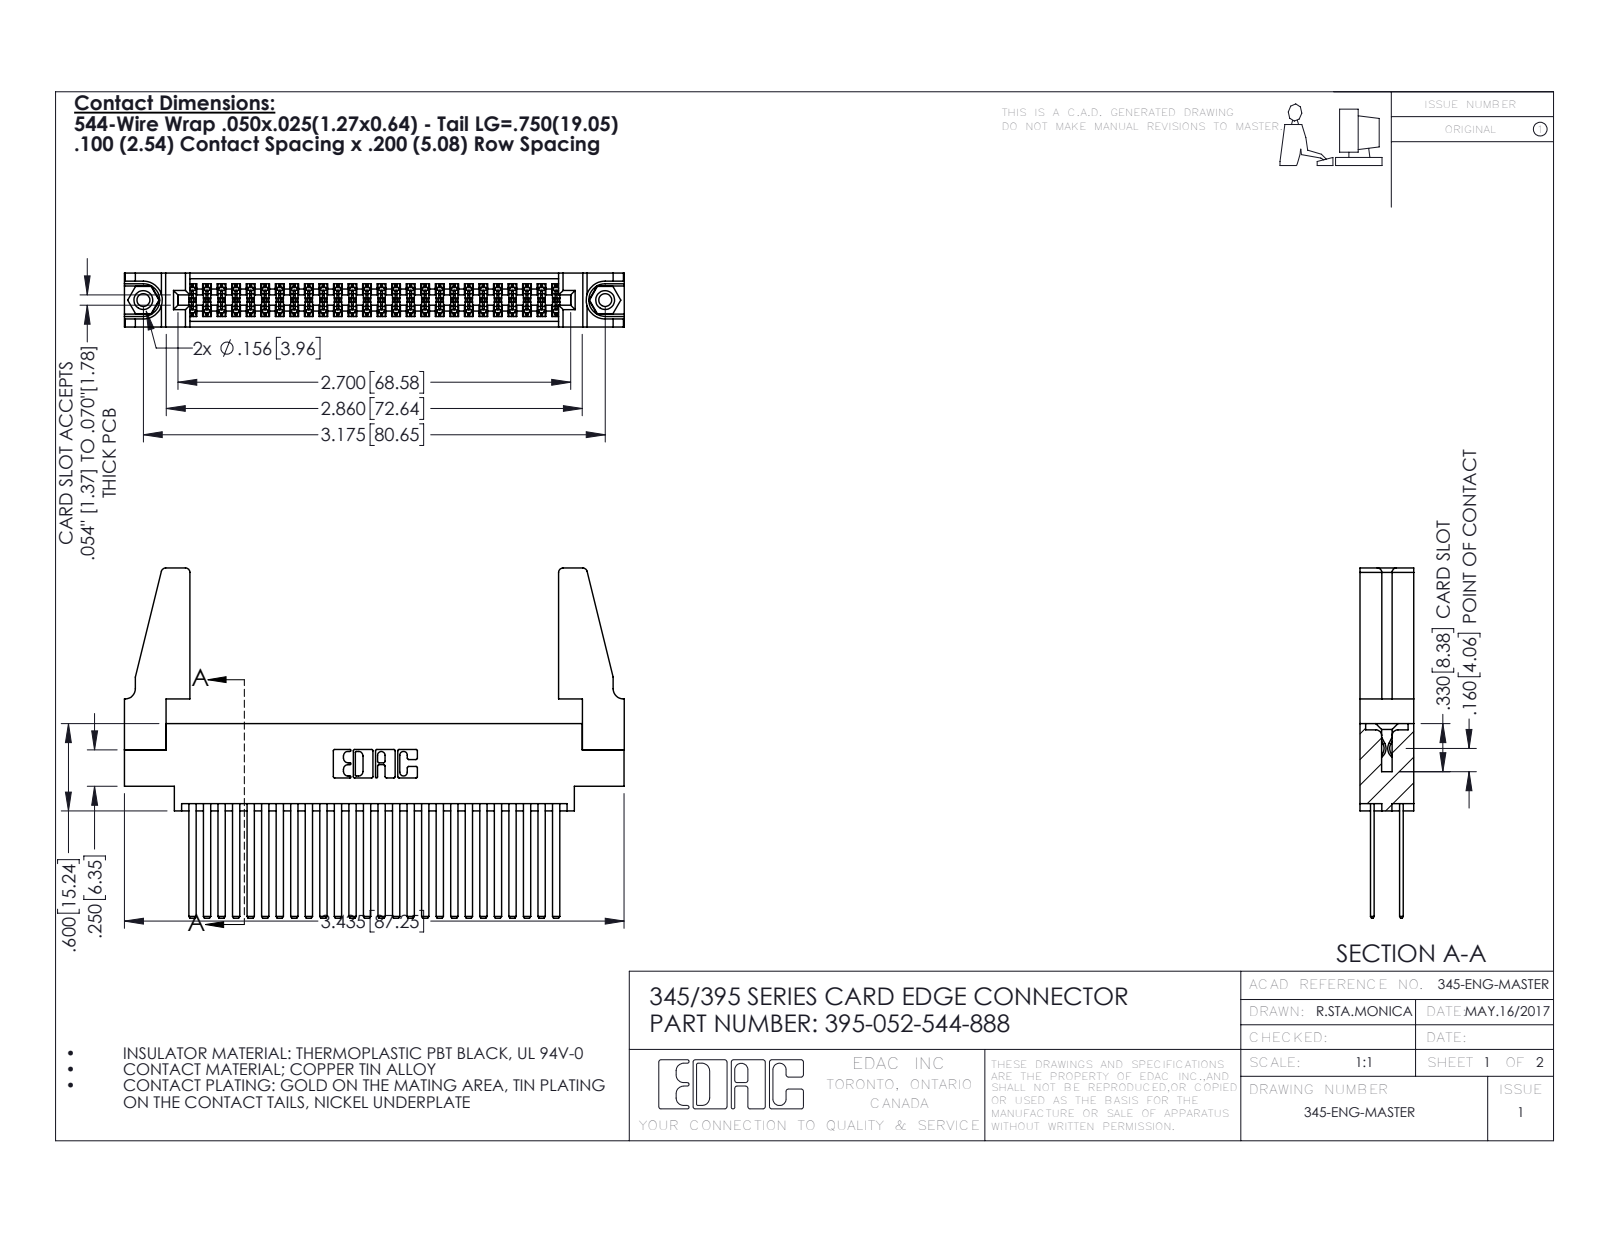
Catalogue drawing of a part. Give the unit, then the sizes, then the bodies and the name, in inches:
Units: inches
Overall size (bounding box): 3.436 × 2.407 × 0.37
Round holes (diameter × count): ⌀0.089 ×2, ⌀0.125 ×2, ⌀0.156 ×2, ⌀0.064 ×1
Round bosses / shafts (diameter × count): ⌀0.155 ×2
Partial cylindrical surfaces — rounded edges, fillets, slot ends (radius × count): R0.006 ×78, R0.01 ×22, R0.03 ×8, R0.007 ×6, R0.031 ×6, R0.026 ×3, R0.014 ×2, R0.019 ×2
Main face-to-face distances: 0.072, 0.298, 0.2, 0.098, 0.272, 0.025, 0.37, 0.225, 0.175, 0.149
Hole centre spacings: 0.27, 2.94, 3.175
Volume: 0.744 in³ · Surface area: 28.39 in²
Bodies: 57 solids, 2542 faces (1664 planar, 862 cylindrical, 16 other)
Part name (STEP PRODUCT): 345-220-078_345-220-088; 345-250-001_345-250-001-102; 395-052-544-888; 345 Part_0.170 Offset - 0.156 Dia-TH (+1 more)
STEP written by: SolidWorks 2016 (CONFIG_CONTROL_DESIGN)
